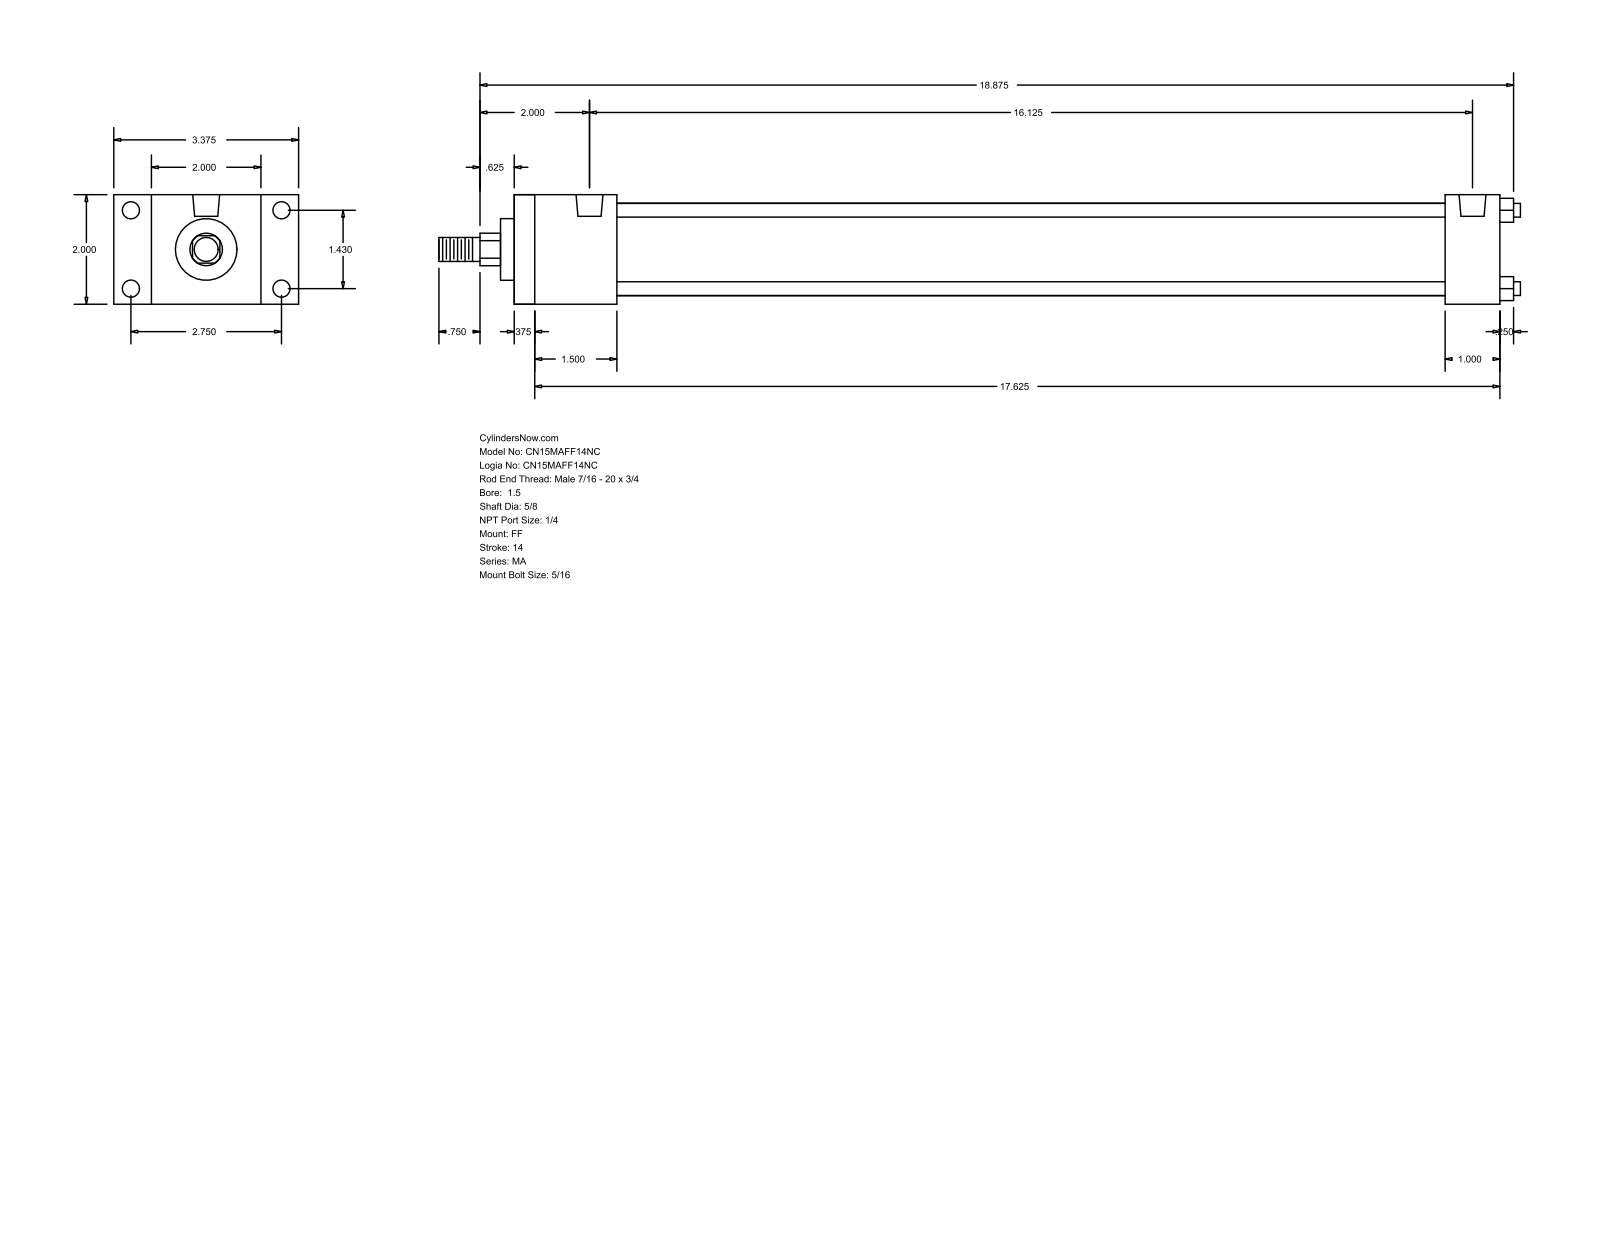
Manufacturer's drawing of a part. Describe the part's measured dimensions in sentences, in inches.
The part is named "MA_FF__0150_0.625". Its 3-D file was written by "GSSL Pune (CONFIG_CONTROL_DESIGN)". It is 0 solids with 92 faces: 64 planar, 28 cylindrical and 0 other. Overall it measures 19.75 by 3.375 by 2 inches. Round holes: 8 of diameter 0.313, 2 of diameter 0.492. Round bosses or shafts: 4 of diameter 0.25, 1 of diameter 1.69, 1 of diameter 1.125, 1 of diameter 0.625, 1 of diameter 0.437. Partial cylindrical surfaces (rounded edges, fillets, slot ends): 1 of radius 0.297. The main face-to-face distances are 2, 18, 0.375, 17.625, 1.875, 17, 1.5, 16.625, 15.125, 16.125. The hole center spacings are 1.43, 2.75, 3.099, 16.125.
